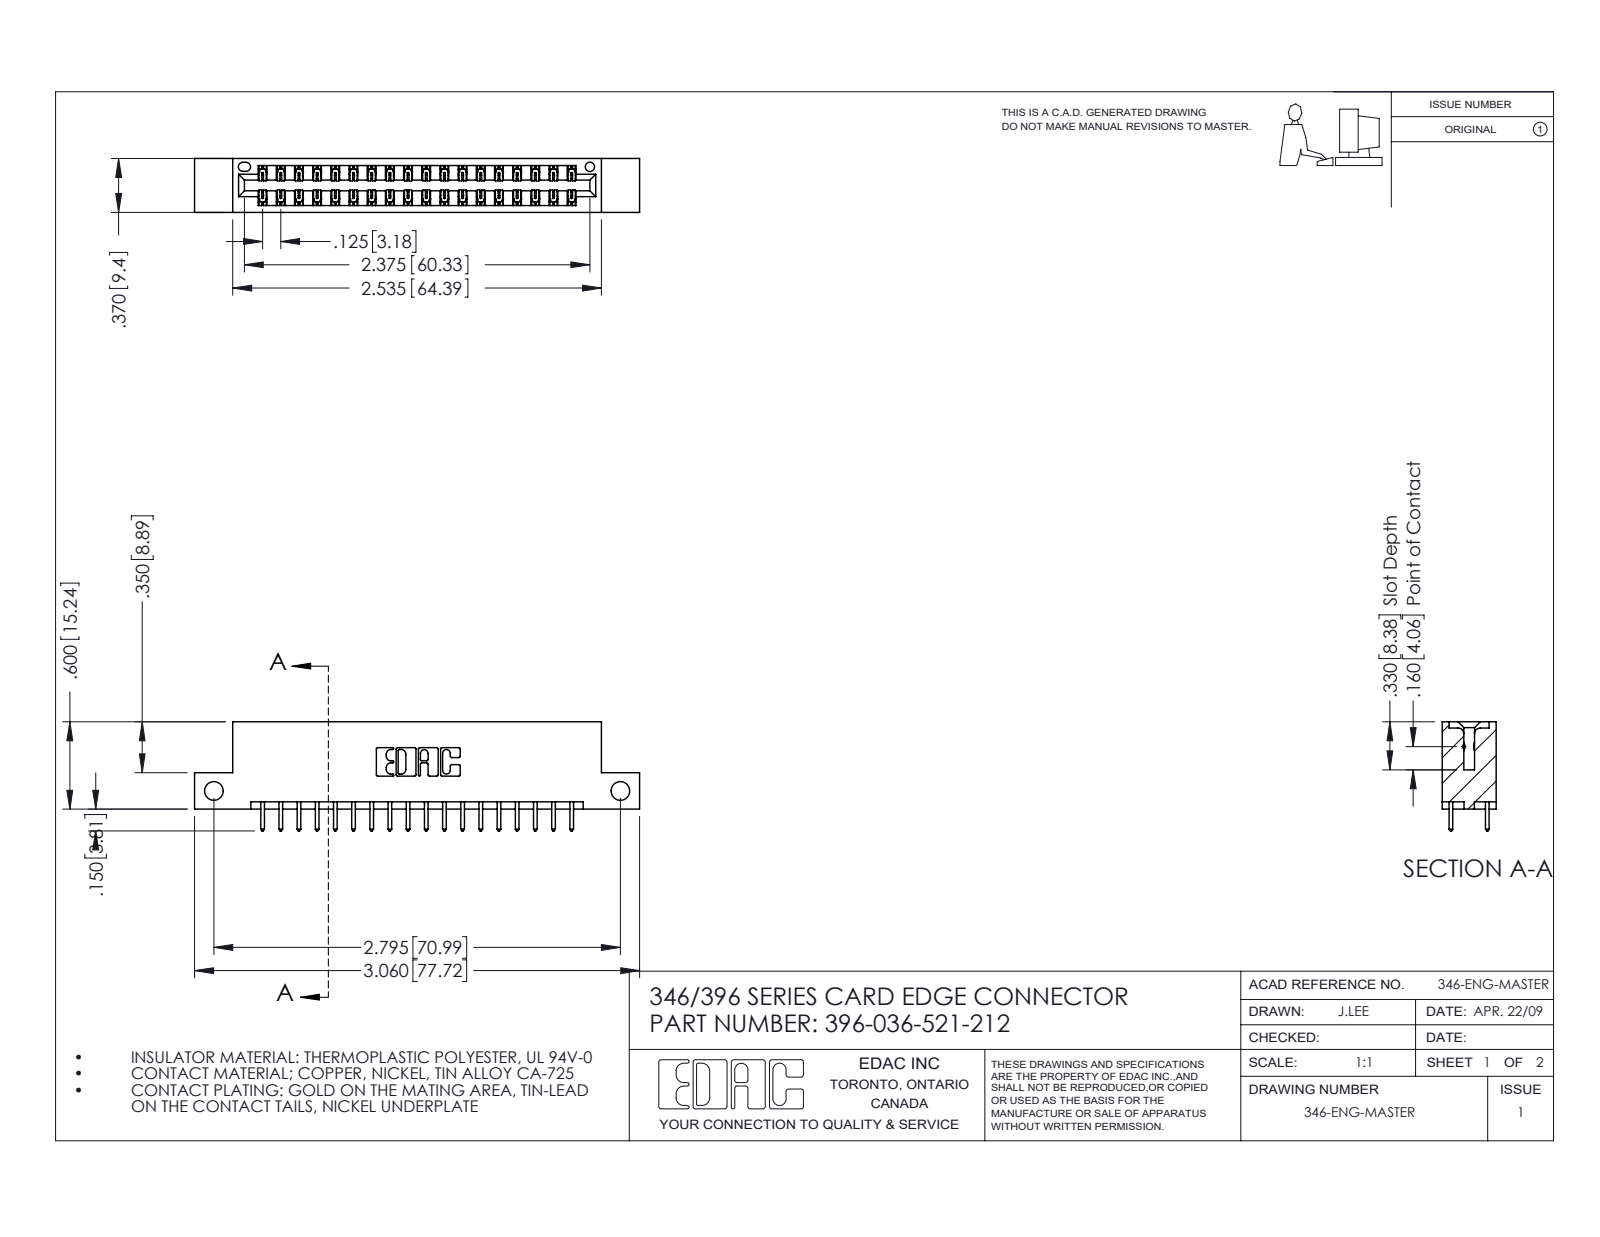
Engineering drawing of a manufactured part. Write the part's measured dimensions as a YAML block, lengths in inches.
part_name: "396-036-521-212; 345-292-001_345-293-121; 346 Part_Flush Mounting Lugs - Side Mount"
step_written_by: "SolidWorks 2016 (CONFIG_CONTROL_DESIGN)"
units: inches
bodies: {solids: 37, faces: 1994, planar: 1336, cylindrical: 658, other: 0}
overall_size: [3.06, 0.75, 0.37]
volume: 0.445
surface_area: 14.58
round_holes:
  - {diameter: 0.128, count: 2}
  - {diameter: 0.064, count: 1}
partial_cylinders:
  - {radius: 0.006, count: 54}
  - {radius: 0.01, count: 36}
  - {radius: 0.01, count: 22}
  - {radius: 0.007, count: 6}
  - {radius: 0.031, count: 6}
  - {radius: 0.026, count: 3}
  - {radius: 0.014, count: 2}
  - {radius: 0.022, count: 2}
face_to_face_distances: [0.048, 0.322, 0.25, 0.37, 0.072, 0.298, 0.025, 0.275, 0.148, 0.222]
hole_center_spacings: [2.795]
